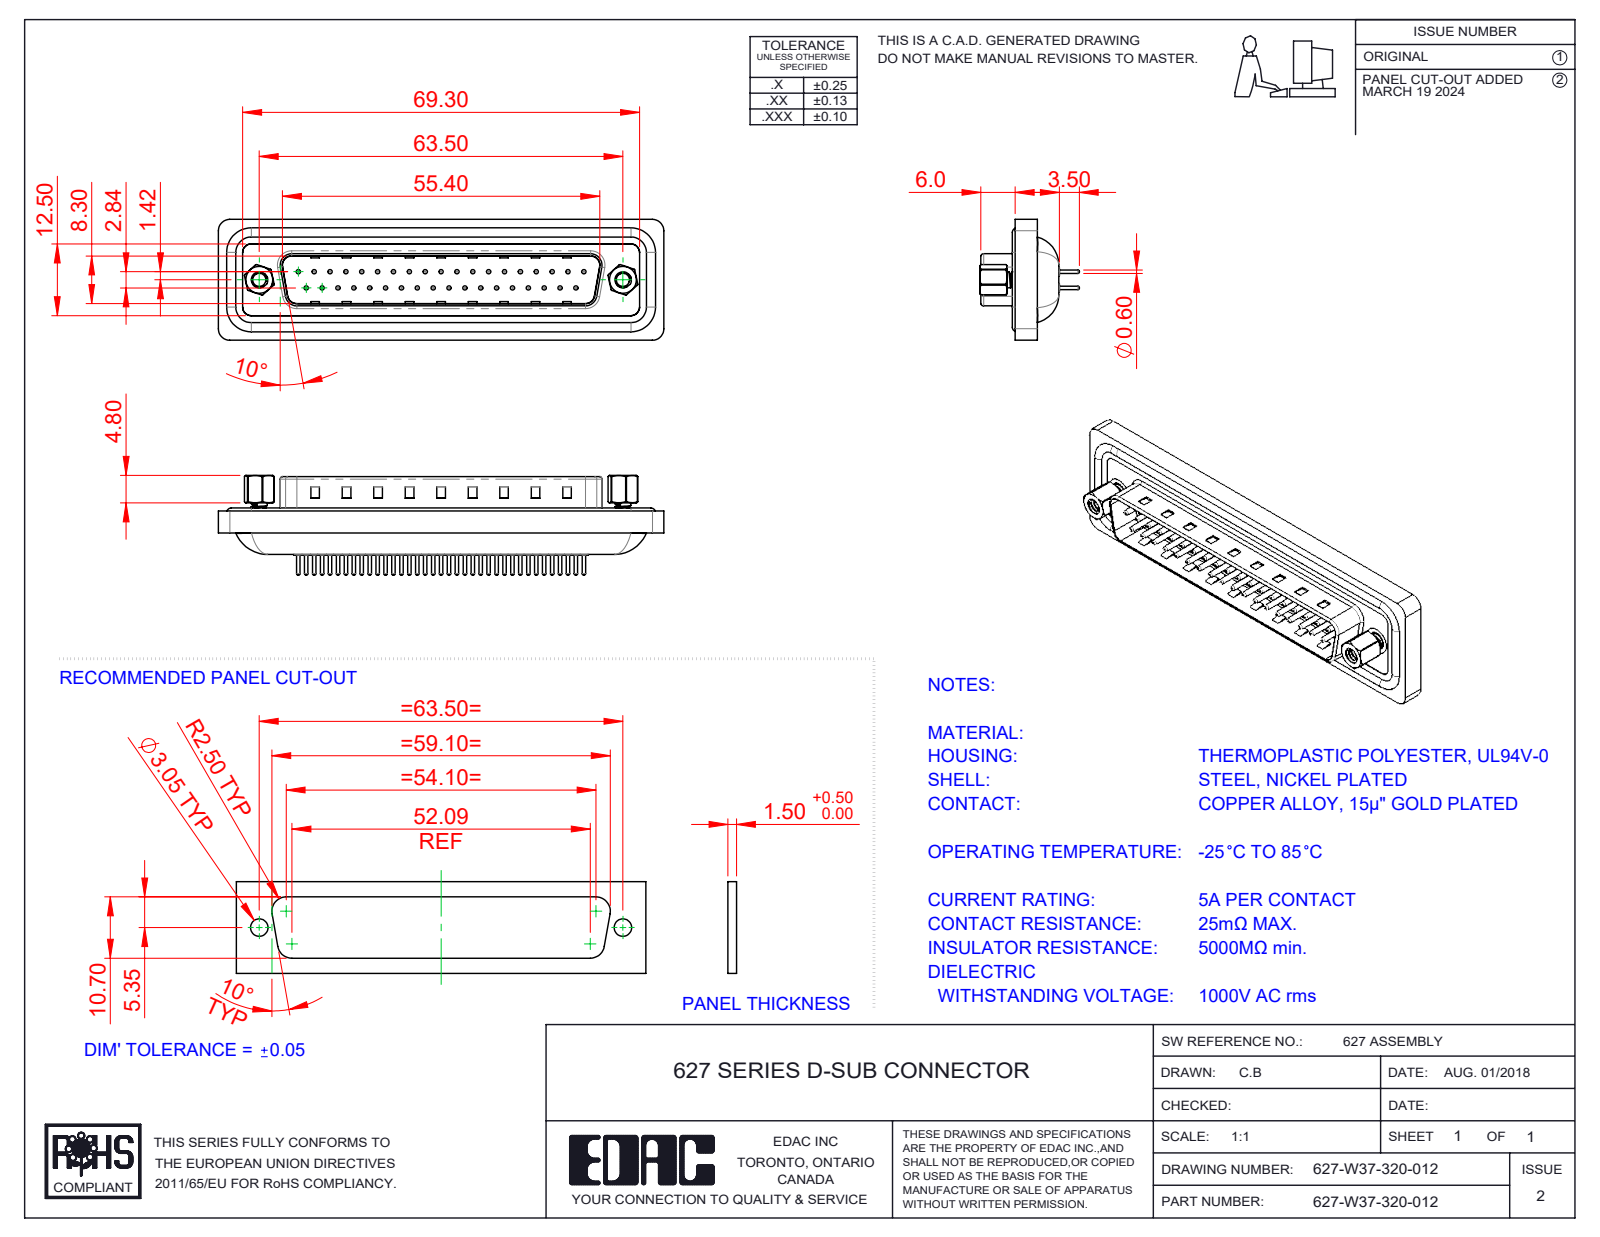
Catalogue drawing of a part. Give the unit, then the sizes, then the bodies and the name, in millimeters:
Units: millimetres
Overall size (bounding box): 77.8 × 21.1 × 17.4
Round holes (diameter × count): ⌀0.75 ×37, ⌀1.5 ×37, ⌀1.6 ×37, ⌀2 ×37, ⌀2.26 ×2, ⌀2.29 ×2, ⌀4 ×2, ⌀4.8 ×2, ⌀5 ×2
Round bosses / shafts (diameter × count): ⌀0.6 ×37, ⌀1.5 ×9, ⌀1.6 ×4, ⌀4.9 ×2, ⌀2.79 ×2
Partial cylindrical surfaces — rounded edges, fillets, slot ends (radius × count): R2 ×16, R1.5 ×14, R0.5 ×8, R2.7 ×6, R0.9 ×4, R1.6 ×4, R4.3 ×4, R0.4 ×2
Main face-to-face distances: 0.75, 0.4, 4.1, 1.1, 2.75, 4.6, 3.75, 5.65, 15.45, 14.7
Hole centre spacings: 3.16, 2.77, 5.54, 8.31, 5.04, 10.1, 11.08, 12.78
Volume: 9 559 mm³ · Surface area: 14 383 mm²
Bodies: 45 solids, 1999 faces (496 planar, 816 cylindrical, 687 other)
Part name (STEP PRODUCT): 627W 4-40 Threaded Rivet; 627W Housing_37 Contacts; 627W Contact Row 2_20; 627W Waterproof Housing_37 Contacts (+4 more)
STEP written by: SolidWorks 2023 (CONFIG_CONTROL_DESIGN)
